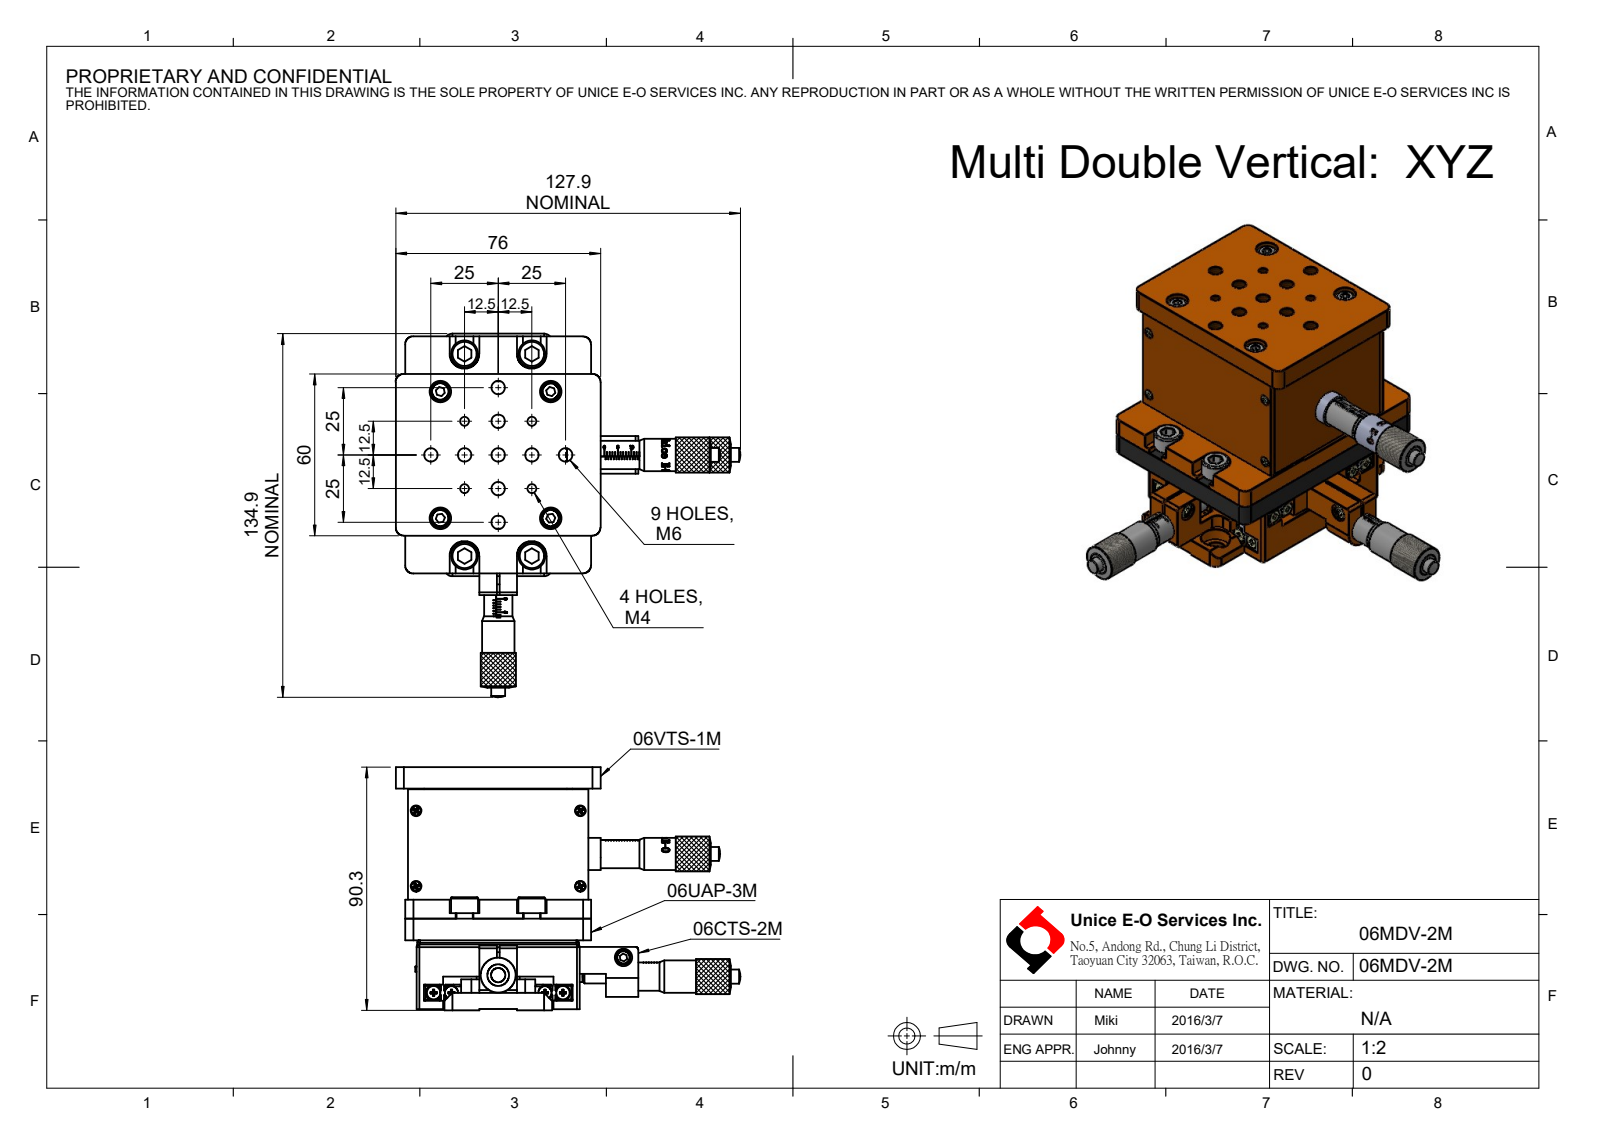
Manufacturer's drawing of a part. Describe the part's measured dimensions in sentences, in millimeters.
The part is named "06MDV-2M". Its 3-D file was written by "SolidWorks 2016 (CONFIG_CONTROL_DESIGN)". It is 127 solids with 4031 faces: 2188 planar, 995 cylindrical and 848 other. Overall it measures 134.9 by 127.9 by 90.25 millimeters. Its volume is 341 932 cubic millimeters and its surface area 175 657 square millimeters. Round holes: 39 of diameter 2.05, 36 of diameter 5, 27 of diameter 2.5, 27 of diameter 3, 12 of diameter 1.6, 12 of diameter 4.8, 11 of diameter 3.3, 9 of diameter 8, 9 of diameter 11, 8 of diameter 4.5, 6 of diameter 3.4, 6 of diameter 6.5. Round bosses or shafts: 22 of diameter 3, 20 of diameter 4.5, 20 of diameter 2.5, 16 of diameter 0.6, 10 of diameter 4, 8 of diameter 5, 8 of diameter 2.55, 7 of diameter 10. Partial cylindrical surfaces (rounded edges, fillets, slot ends): 20 of radius 1, 14 of radius 3, 8 of radius 3.1, 4 of radius 1.5, 4 of radius 3.3, 1 of radius 2.5, 1 of radius 5.98, 1 of radius 7. The main face-to-face distances are 8, 56.25, 6, 48.25, 7, 41.25, 2, 55, 16.5, 0.5. The hole center spacings are 25, 39.53, 20, 17.68, 8.62, 12.5, 13.2, 17.06.
